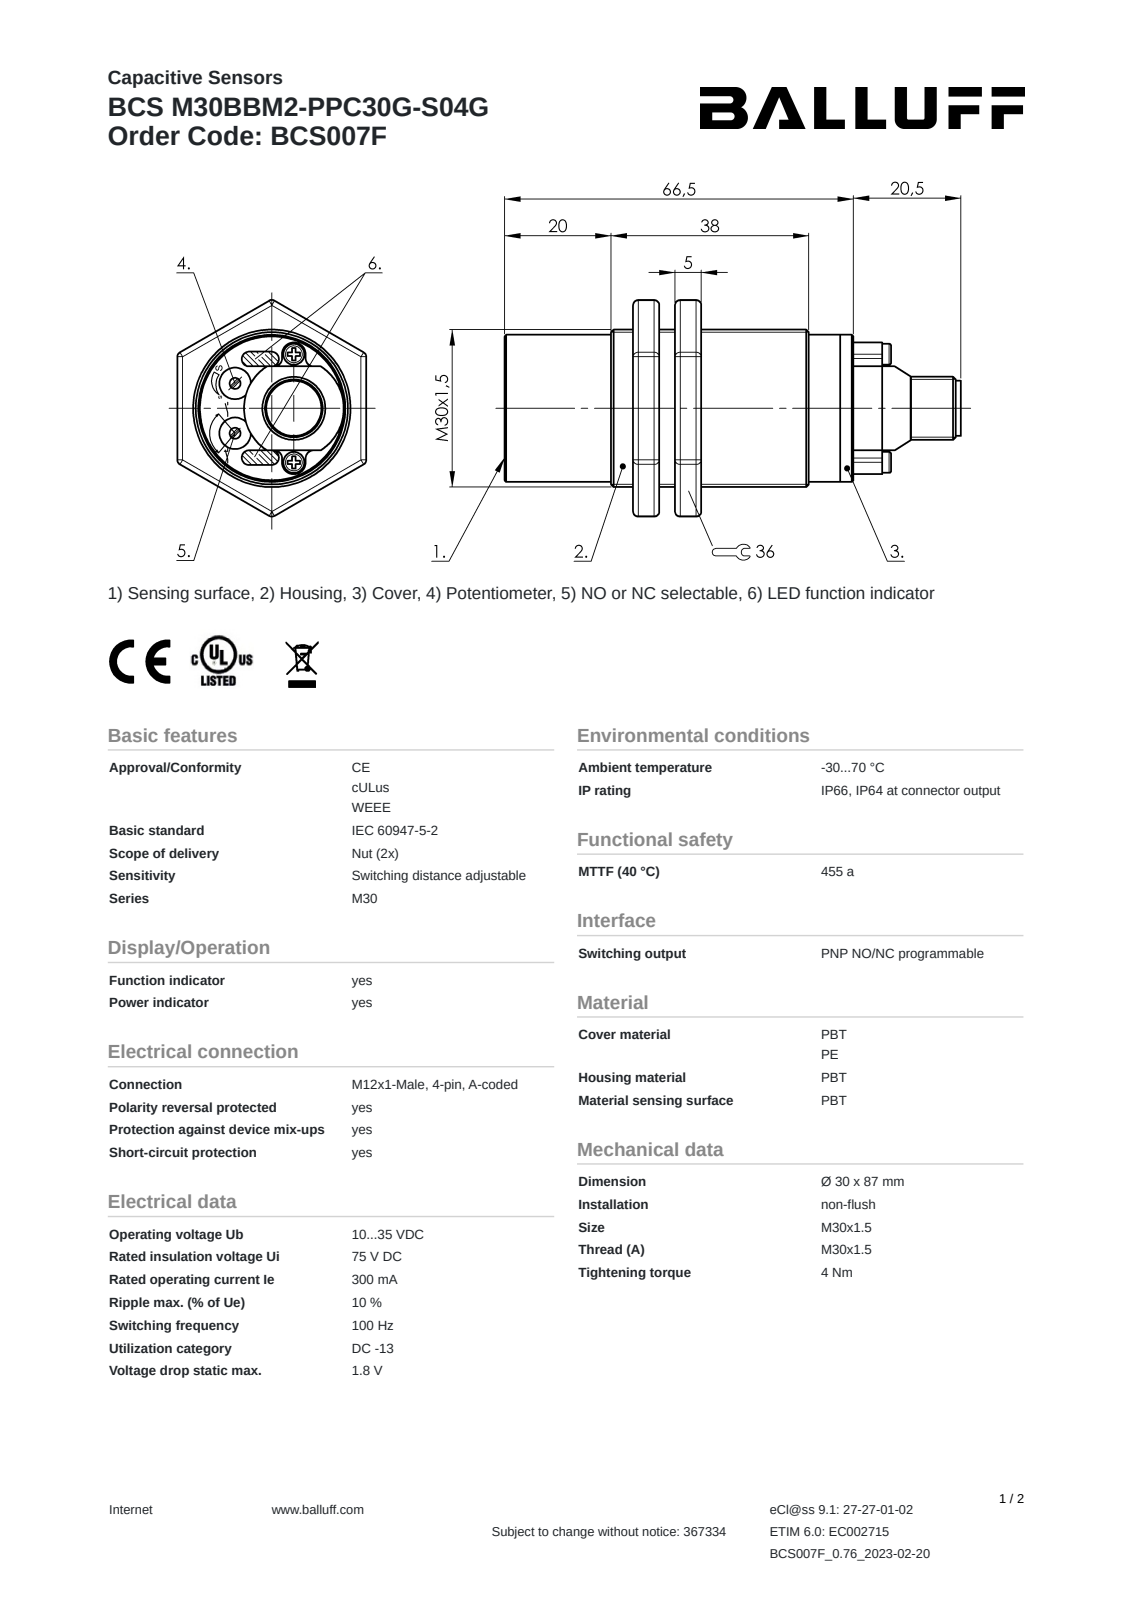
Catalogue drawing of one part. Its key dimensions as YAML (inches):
part_name: "BCS007F"
step_written_by: "SolidWorks 2021 (AUTOMOTIVE_DESIGN)"
units: inches
bodies: {solids: 3, faces: 159, planar: 86, cylindrical: 33, other: 40}
overall_size: [3.425, 1.637, 1.417]
volume: 3.189
surface_area: 19.32
round_holes:
  - {diameter: 0.098, count: 2}
  - {diameter: 0.197, count: 2}
  - {diameter: 0.327, count: 1}
  - {diameter: 1.117, count: 1}
round_bosses_or_shafts:
  - {diameter: 0.039, count: 4}
  - {diameter: 0.157, count: 2}
  - {diameter: 1.181, count: 1}
  - {diameter: 1.102, count: 1}
  - {diameter: 1.094, count: 1}
  - {diameter: 0.472, count: 1}
  - {diameter: 0.409, count: 1}
partial_cylinders:
  - {radius: 0.05, count: 4}
  - {radius: 0.059, count: 4}
  - {radius: 0.089, count: 2}
  - {radius: 0.024, count: 1}
  - {radius: 0.369, count: 1}
  - {radius: 0.374, count: 1}
face_to_face_distances: [0.315, 0.197, 1.417, 1.28, 1.476, 0.512, 0.965, 0.118, 1.161, 1.142]
hole_center_spacings: [0.333, 0.479, 0.165, 0.374]
